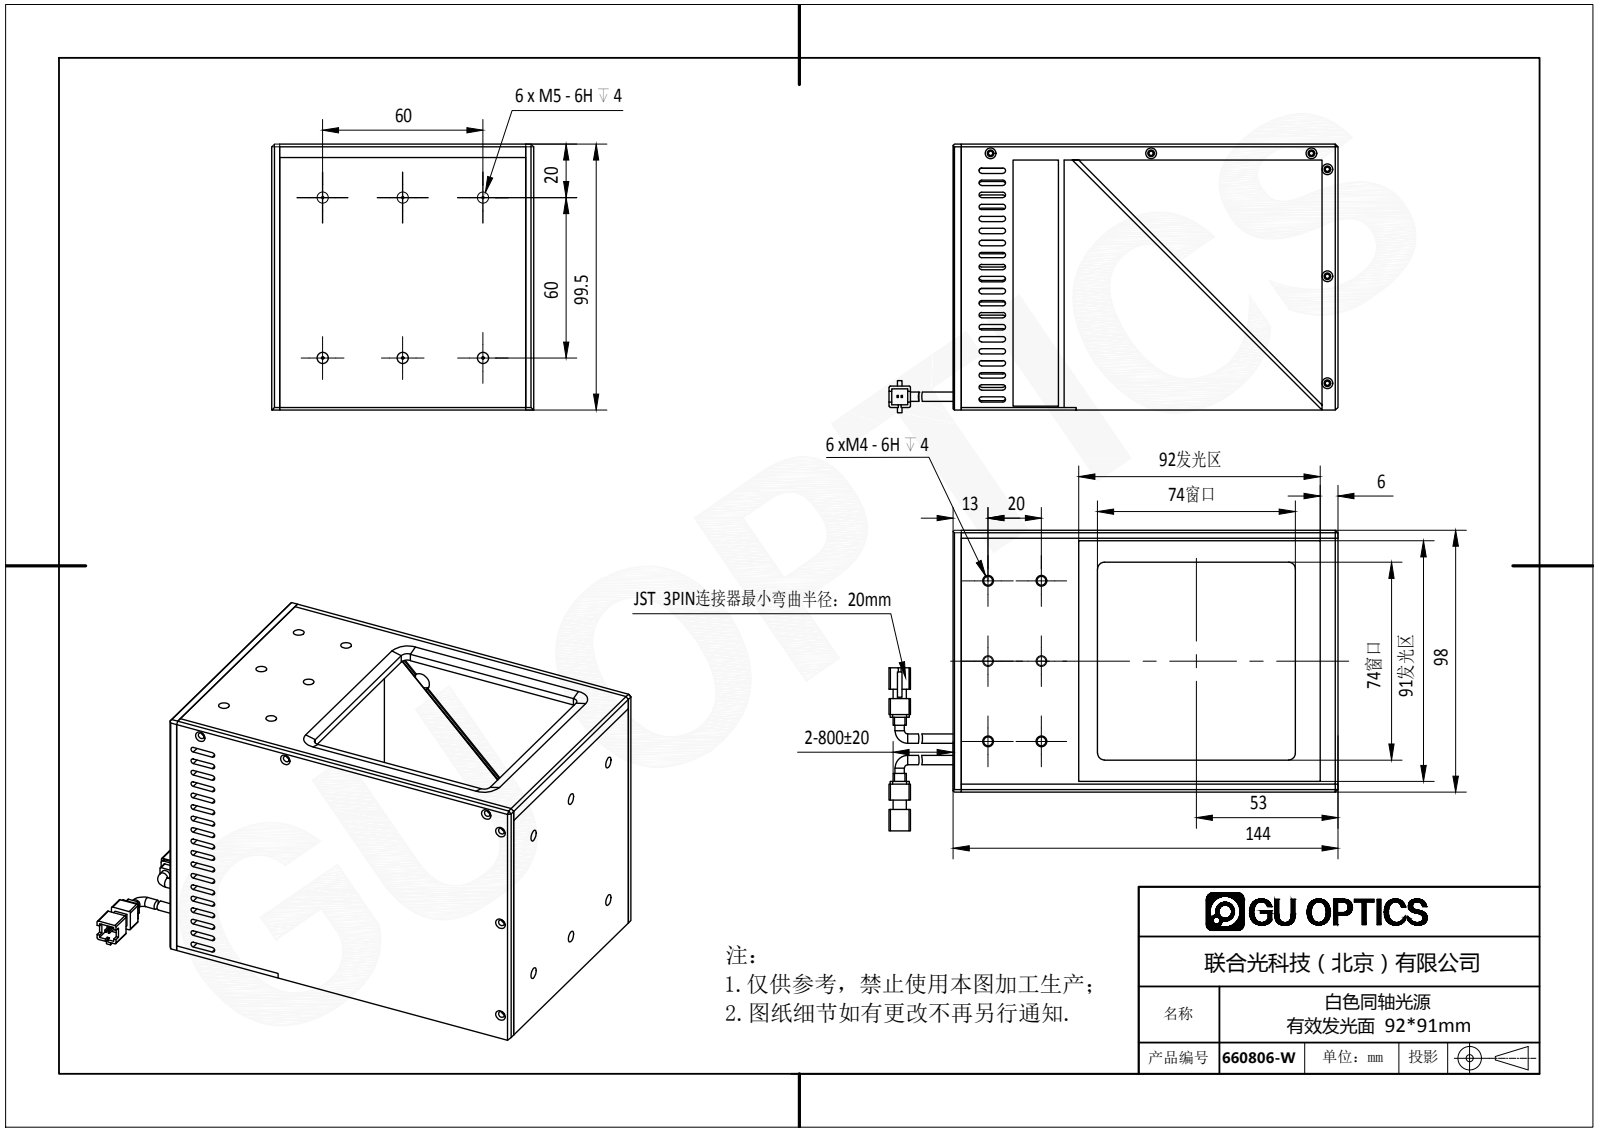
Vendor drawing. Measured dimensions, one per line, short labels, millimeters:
name: 白色同轴光源 有效发光面 9291mm
written by: SolidWorks 2016 (AUTOMOTIVE_DESIGN)
unit: mm
bodies: 22 solids, 4262 faces (906 planar, 2251 cylindrical, 1105 other)
size: 168 × 110.5 × 99.7
volume: 274 829 mm³; area: 199 655 mm²
holes: 16× ⌀1.6, 16× ⌀2.4, 14× ⌀2, 6× ⌀3.3, 6× ⌀4, 6× ⌀4.2, 4× ⌀2.5, 4× ⌀7, 2× ⌀1, 2× ⌀6.8, 1× ⌀38, 1× ⌀48
bosses: 462× ⌀3.8, 462× ⌀3, 3× ⌀3.5, 1× ⌀51, 1× ⌀41
rounds: 76× R1, 8× R0.5, 8× R1.76, 8× R1.76, 8× R1.77, 8× R2, 4× R2.5, 2× R1.01
face distances: 4, 94, 2, 3, 98, 6, 90, 1, 141, 135
hole spacings: 30, 60, 50, 23.41, 35.36, 36.06, 67.08, 72.1
